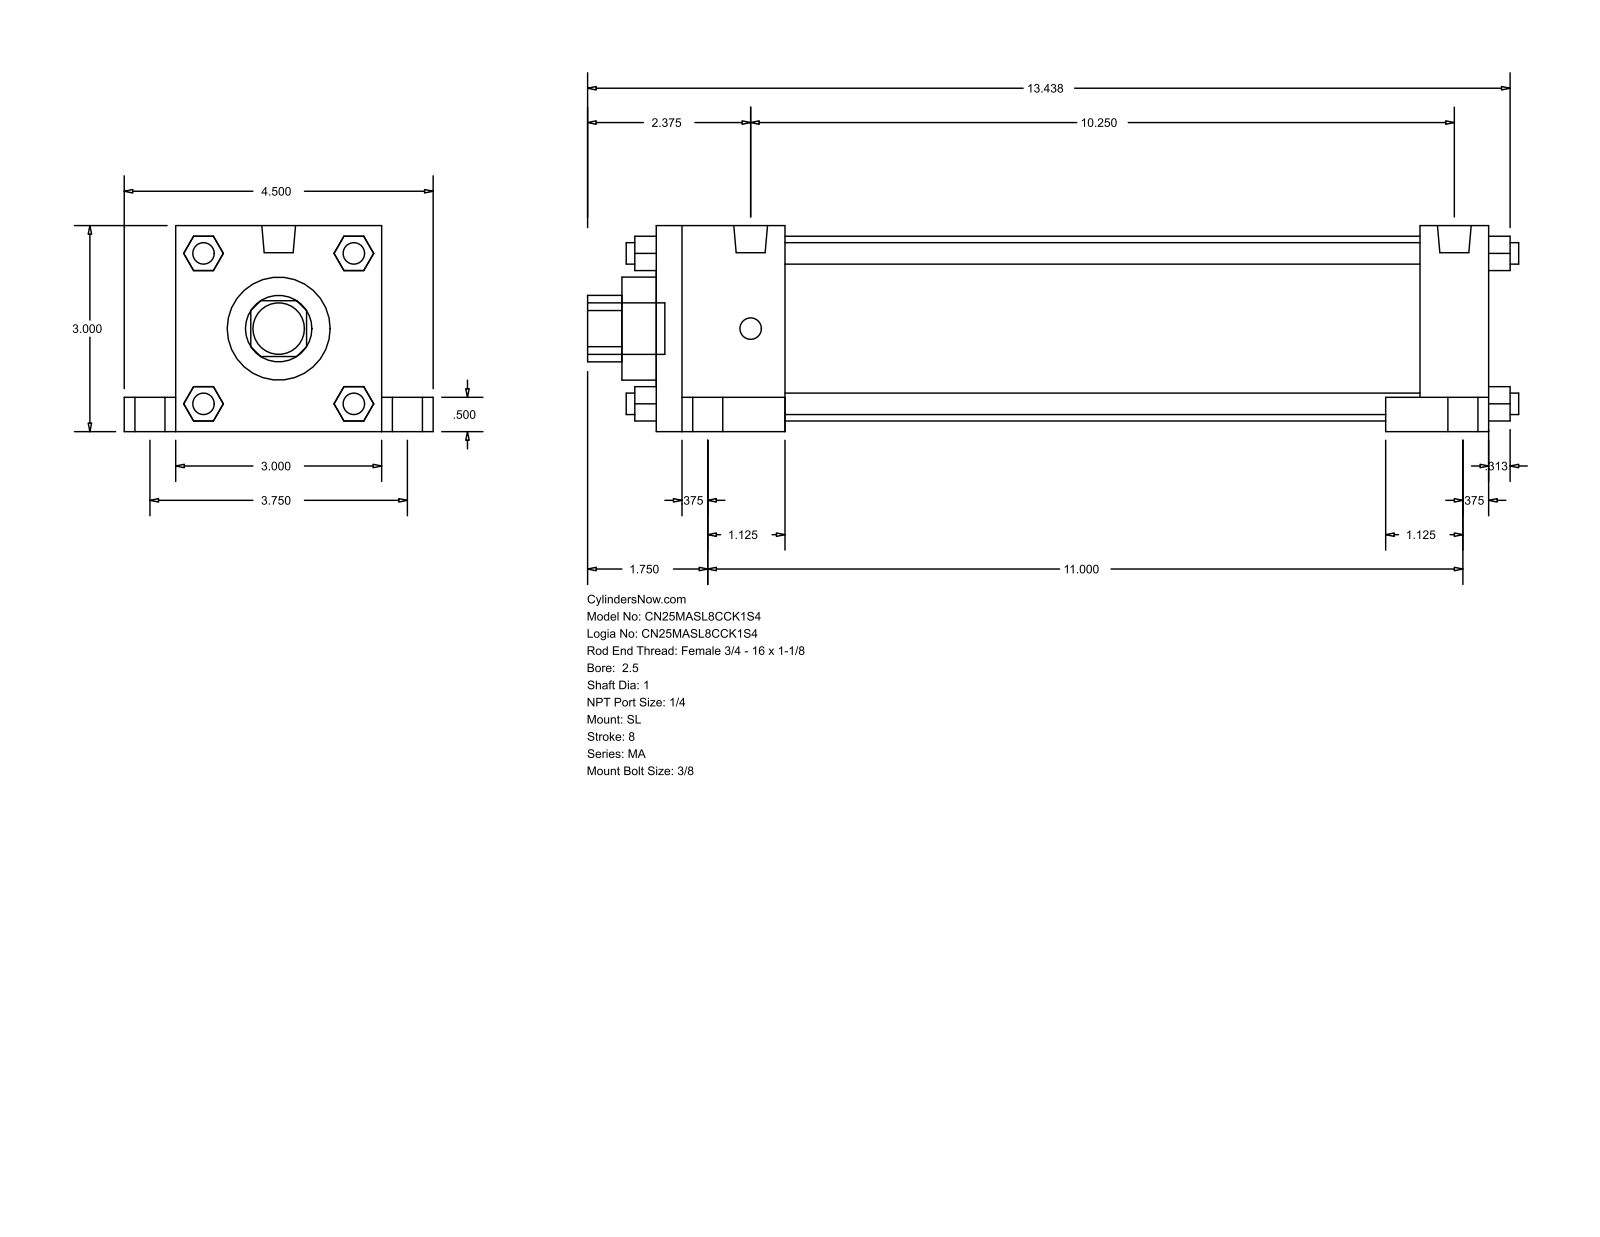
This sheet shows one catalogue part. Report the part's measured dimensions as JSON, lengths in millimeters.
{"part_name": "MA_SL__0250_1", "step_written_by": "GSSL Pune (CONFIG_CONTROL_DESIGN)", "units": "millimeters", "bodies": {"solids": 0, "faces": 148, "planar": 112, "cylindrical": 36, "other": 0}, "overall_size": [344.49, 114.3, 76.2], "round_holes": [[25.4, 1], [38.1, 1], [68.33, 1]], "round_bosses_or_shafts": [[7.94, 8], [17.46, 4], [11.11, 4], [12.49, 2], [19.05, 1]], "partial_cylinders_radius": [[12.29, 1]], "face_to_face_distances": [76.2, 307.98, 12.7, 234.95, 25.4, 47.63, 260.35, 282.58, 19.05, 95.25]}
